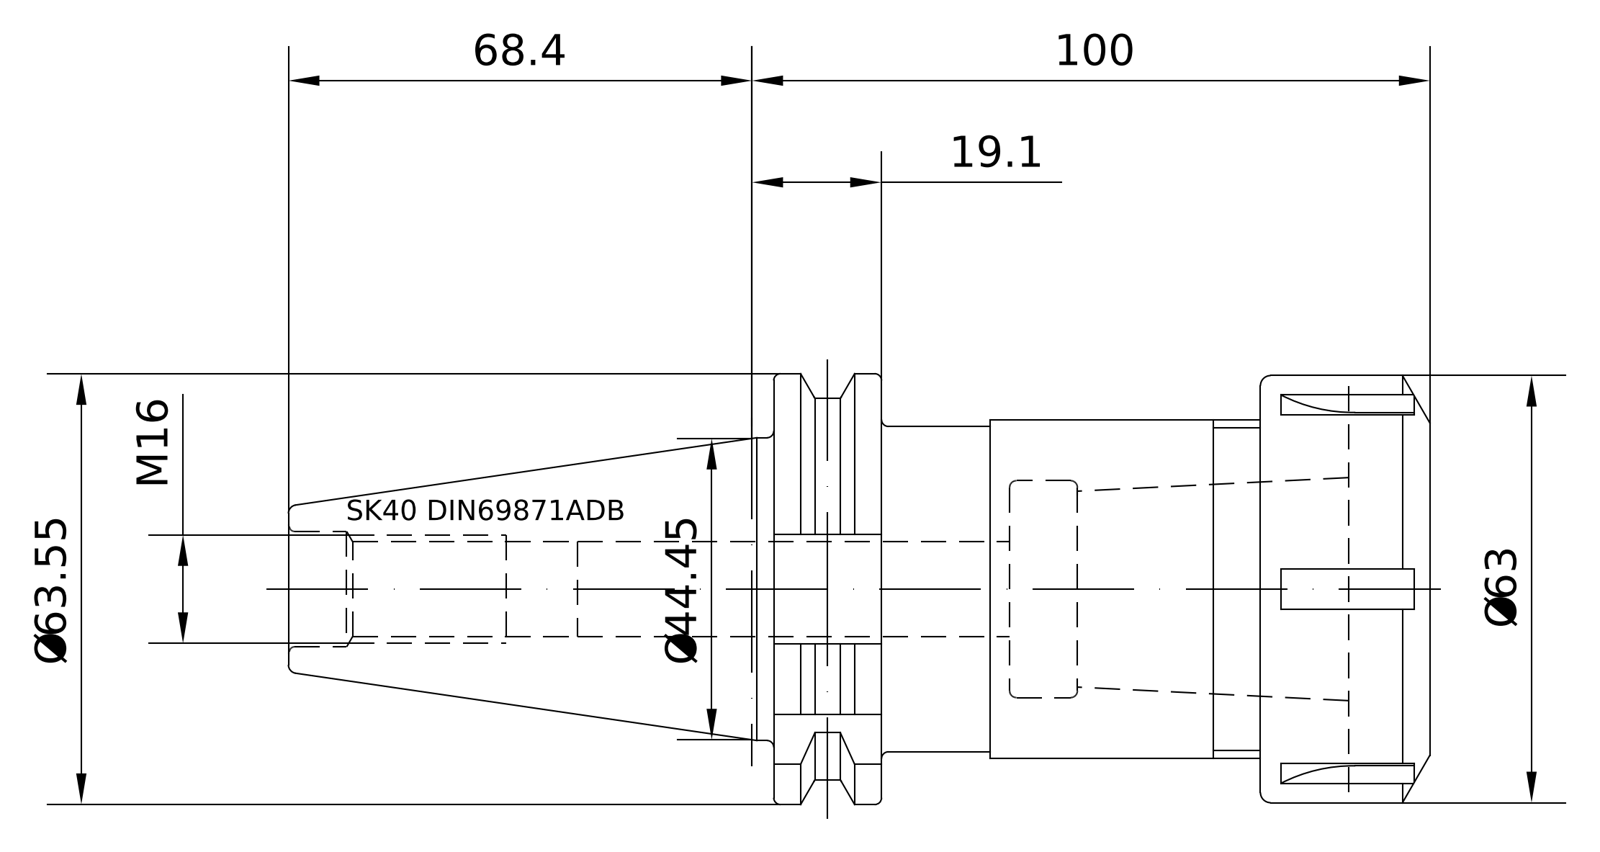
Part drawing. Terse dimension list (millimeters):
name: 40-321-40; 83-912-40; 40-321-40_ASM
written by: PRO/ENGINEER BY PARAMETRIC TECHNOLOGY CORPORATION, 2010430 (CONFIG_CONTROL_DESIGN)
unit: mm
bodies: 2 solids, 141 faces (50 planar, 34 cylindrical, 57 other)
size: 168.25 × 63.52 × 63
volume: 271 441 mm³; area: 44 965 mm²
holes: 1× ⌀13.84, 1× ⌀17.01, 1× ⌀17.5, 1× ⌀30.5
bosses: 1× ⌀63, 1× ⌀50, 1× ⌀47.5, 1× ⌀43.75, 1× ⌀16.01
rounds: 6× R2.7, 1× R1.35, 1× R28, 1× R31.76
face distances: 25.5, 71.3, 96.8, 15.85, 55.45, 80.95, 43.8, 27.95, 27.5, 53
